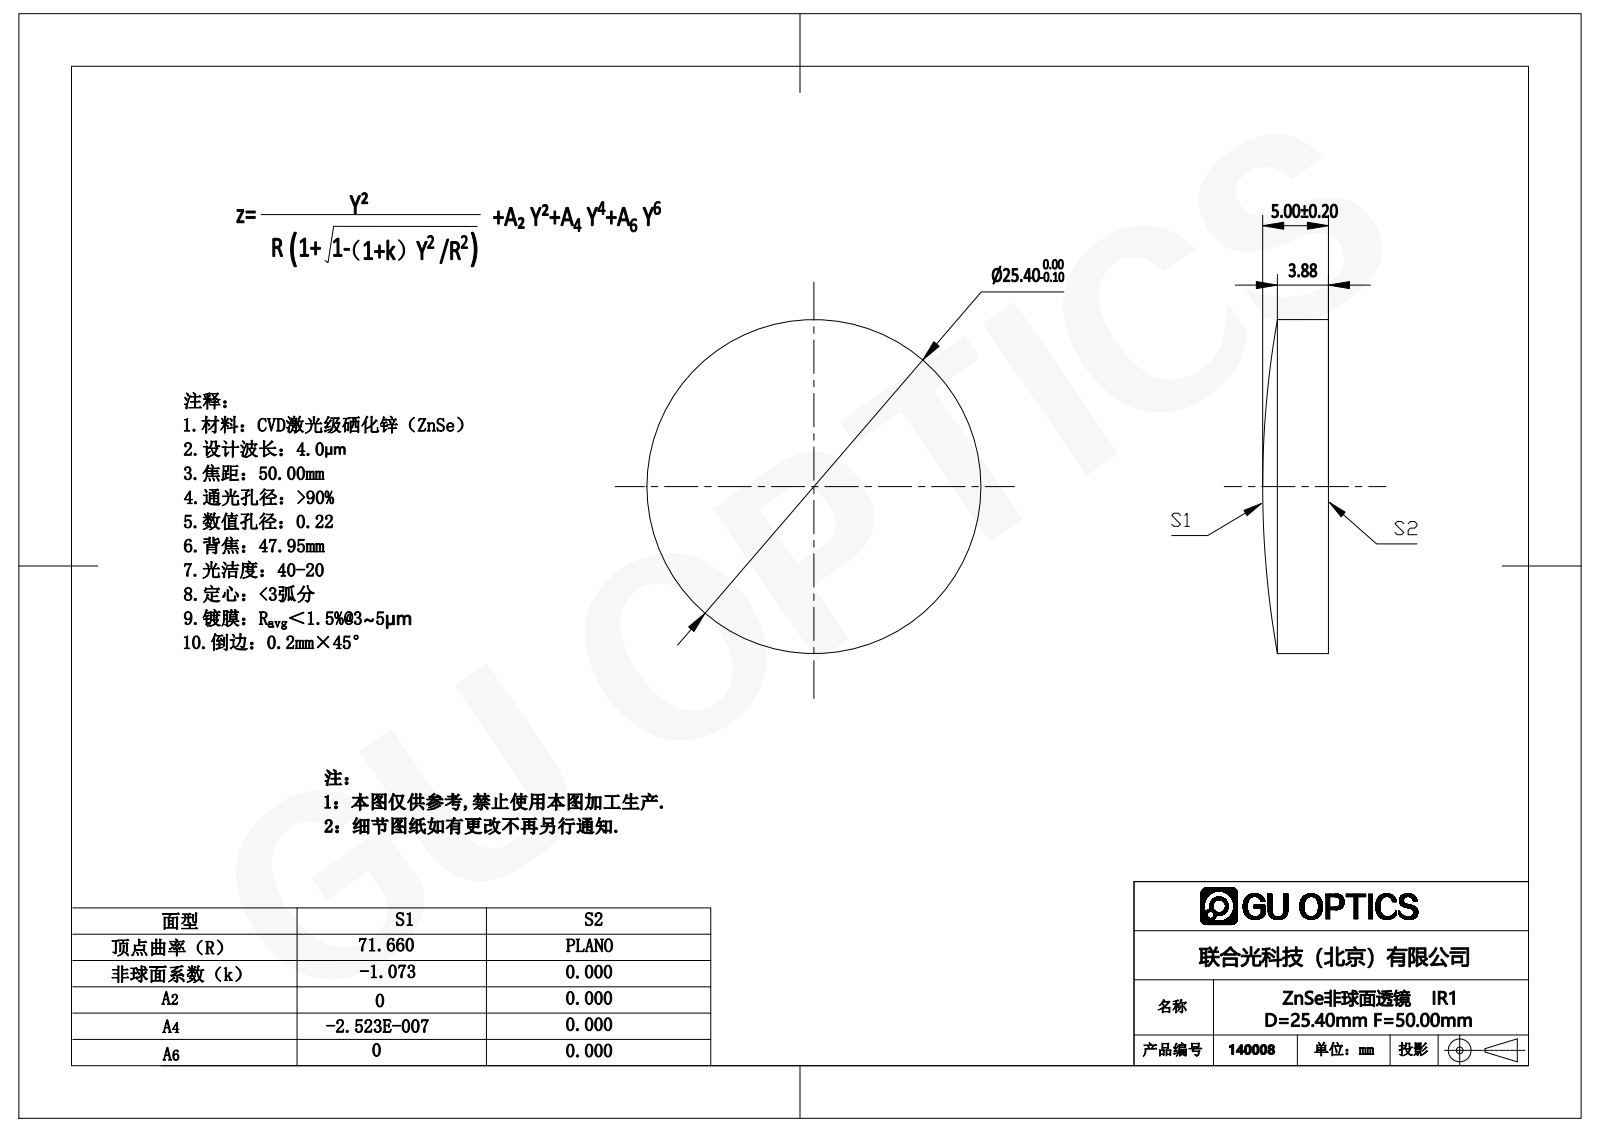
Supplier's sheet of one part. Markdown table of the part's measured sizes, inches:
| quantity | value |
| --- | --- |
| part name | 140008 |
| STEP written by | SolidWorks 2020 (CONFIG_CONTROL_DESIGN) |
| units | inches |
| bodies | 1 solid, 5 faces (1 planar, 2 cylindrical, 2 other) |
| overall size | 1 × 1 × 0.197 |
| volume | 0.137 in³ |
| surface area | 2.057 in² |
| round bosses / shafts (diameter × count) | 1 × 1 |
